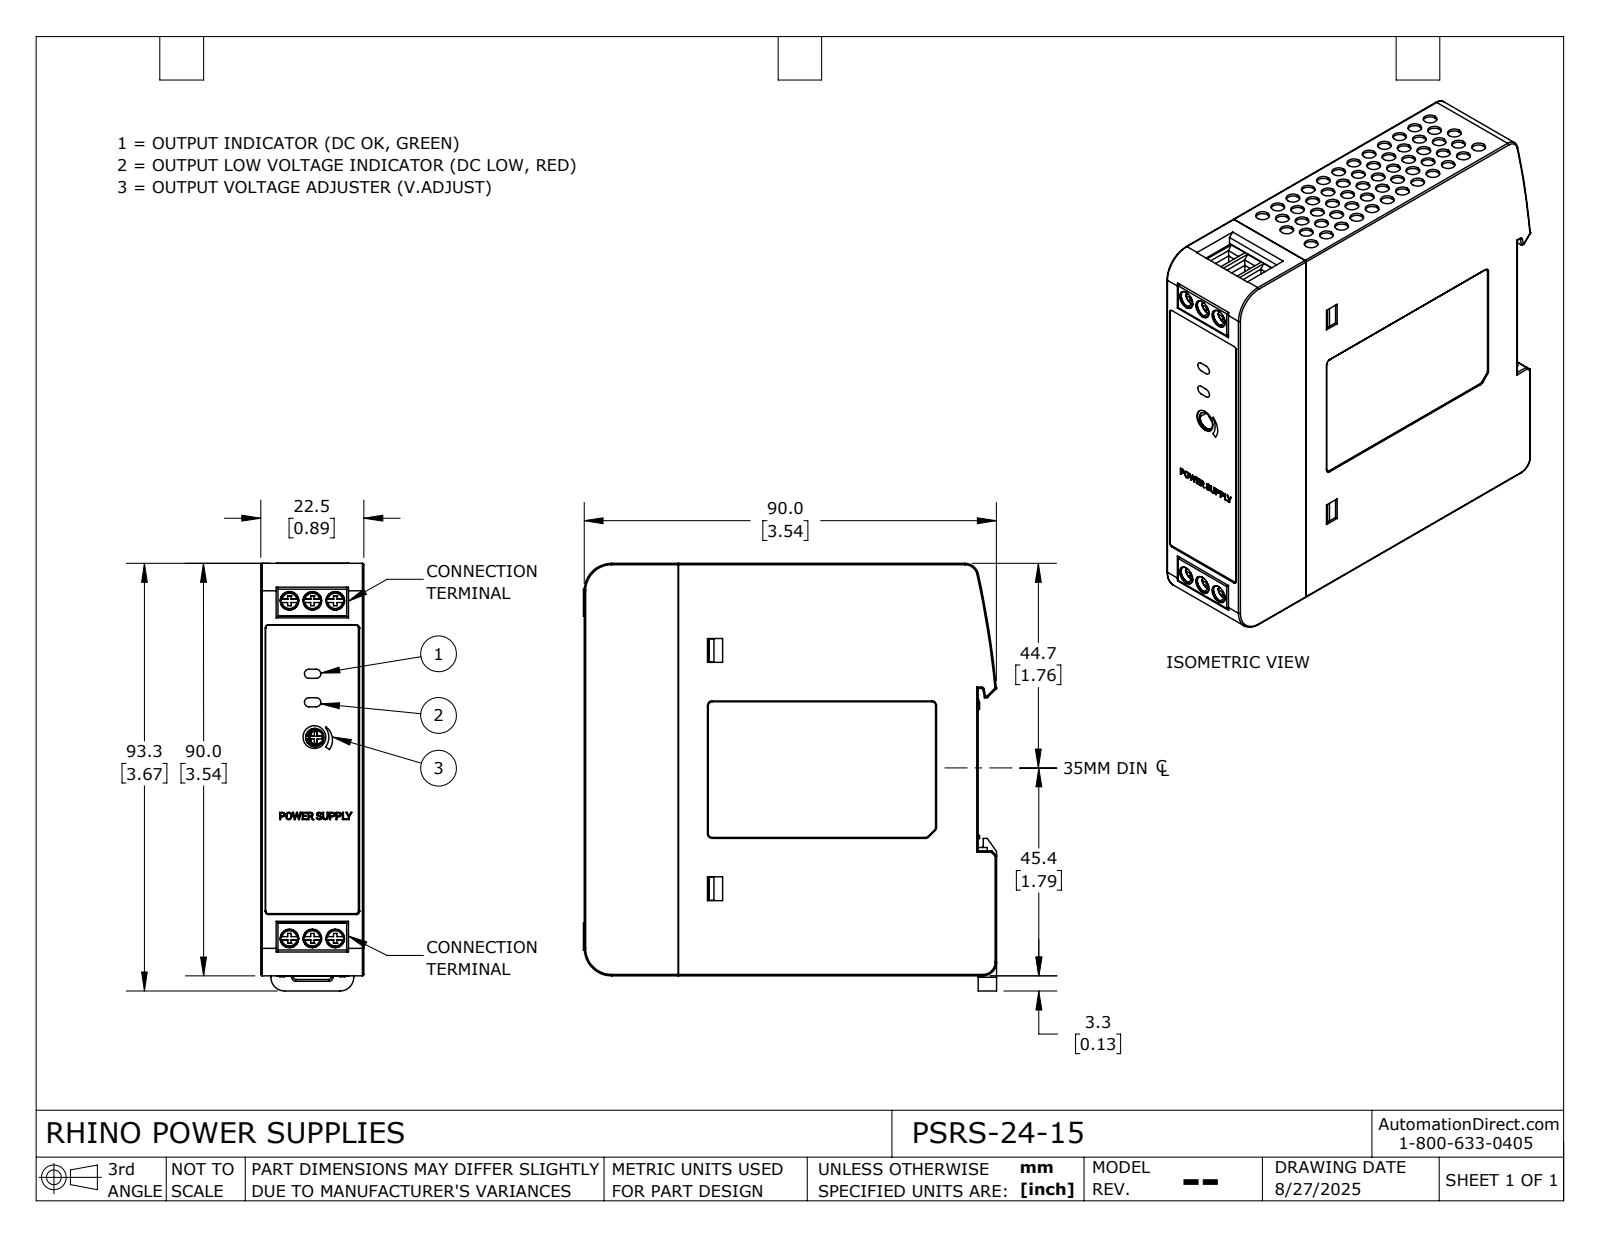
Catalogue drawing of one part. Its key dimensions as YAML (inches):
part_name: "PSRS-24-15"
step_written_by: "SolidWorks 2024 (AUTOMOTIVE_DESIGN)"
units: inches
bodies: {solids: 1, faces: 1156, planar: 635, cylindrical: 183, other: 338}
overall_size: [3.673, 3.55, 0.886]
volume: 10.63
surface_area: 44.53
round_holes:
  - {diameter: 0.15, count: 6}
  - {diameter: 0.159, count: 6}
  - {diameter: 0.157, count: 3}
  - {diameter: 0.134, count: 1}
round_bosses_or_shafts:
  - {diameter: 0.156, count: 6}
  - {diameter: 0.118, count: 1}
  - {diameter: 0.079, count: 1}
partial_cylinders:
  - {radius: 0.012, count: 48}
  - {radius: 0.039, count: 11}
  - {radius: 0.004, count: 8}
  - {radius: 0.118, count: 8}
  - {radius: 0.02, count: 7}
  - {radius: 0.098, count: 3}
  - {radius: 0.024, count: 2}
  - {radius: 0.043, count: 2}
face_to_face_distances: [0.886, 0.88, 3.543, 3.38, 0.02, 3.524, 0.157, 0.079, 3.537, 0.602]
hole_center_spacings: [0.197, 2.905, 2.898, 0.394, 1.174, 2.925, 0.244, 0.3]
